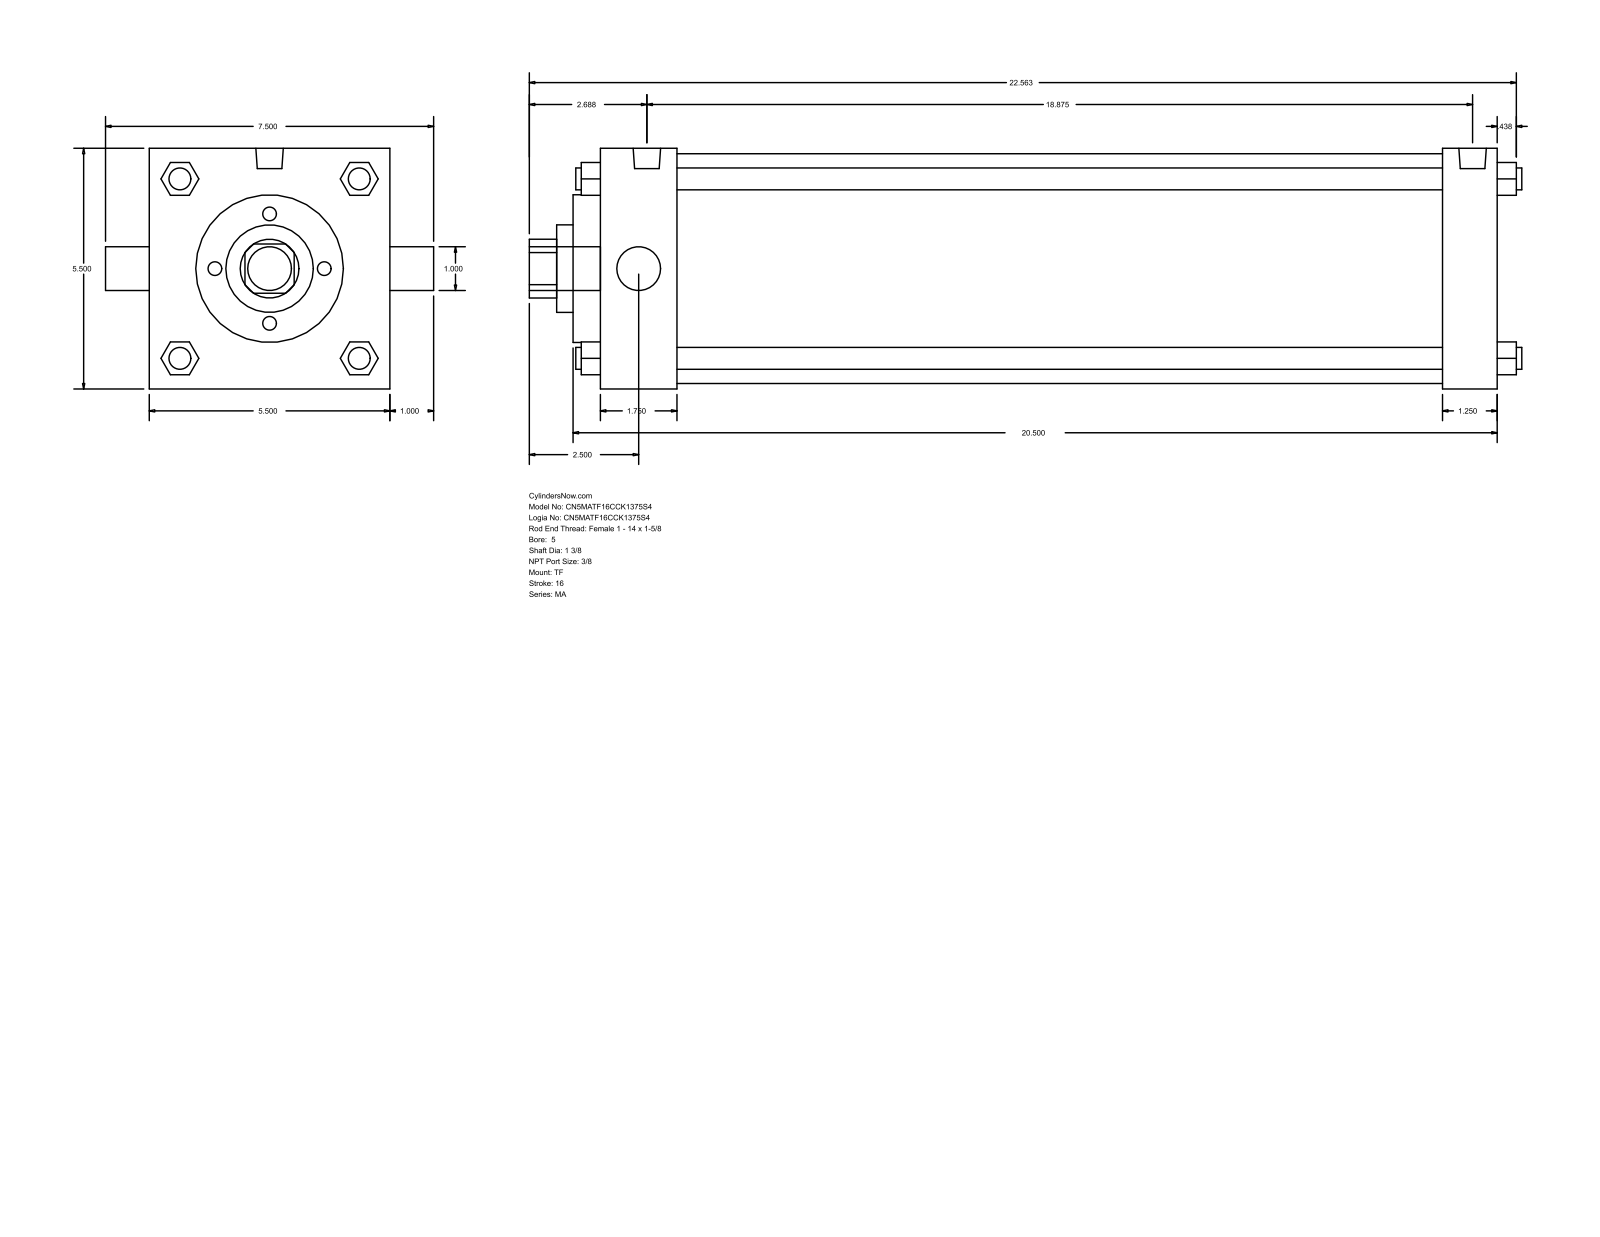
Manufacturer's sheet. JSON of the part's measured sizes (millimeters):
{"part_name": "MA_TF__0500_1.375", "step_written_by": "GSSL Pune (CONFIG_CONTROL_DESIGN)", "units": "millimeters", "bodies": {"solids": 0, "faces": 122, "planar": 93, "cylindrical": 29, "other": 0}, "overall_size": [576.26, 190.5, 139.7], "round_holes": [[25.4, 1], [34.92, 1], [50.8, 1], [85.72, 1], [133.35, 1]], "round_bosses_or_shafts": [[12.7, 4], [11.11, 3], [15.93, 2], [25.4, 1]], "partial_cylinders_radius": [[17.06, 1]], "face_to_face_distances": [139.7, 520.71, 488.96, 31.75, 44.45, 444.51, 476.26, 15.87, 60.32, 504.83]}
